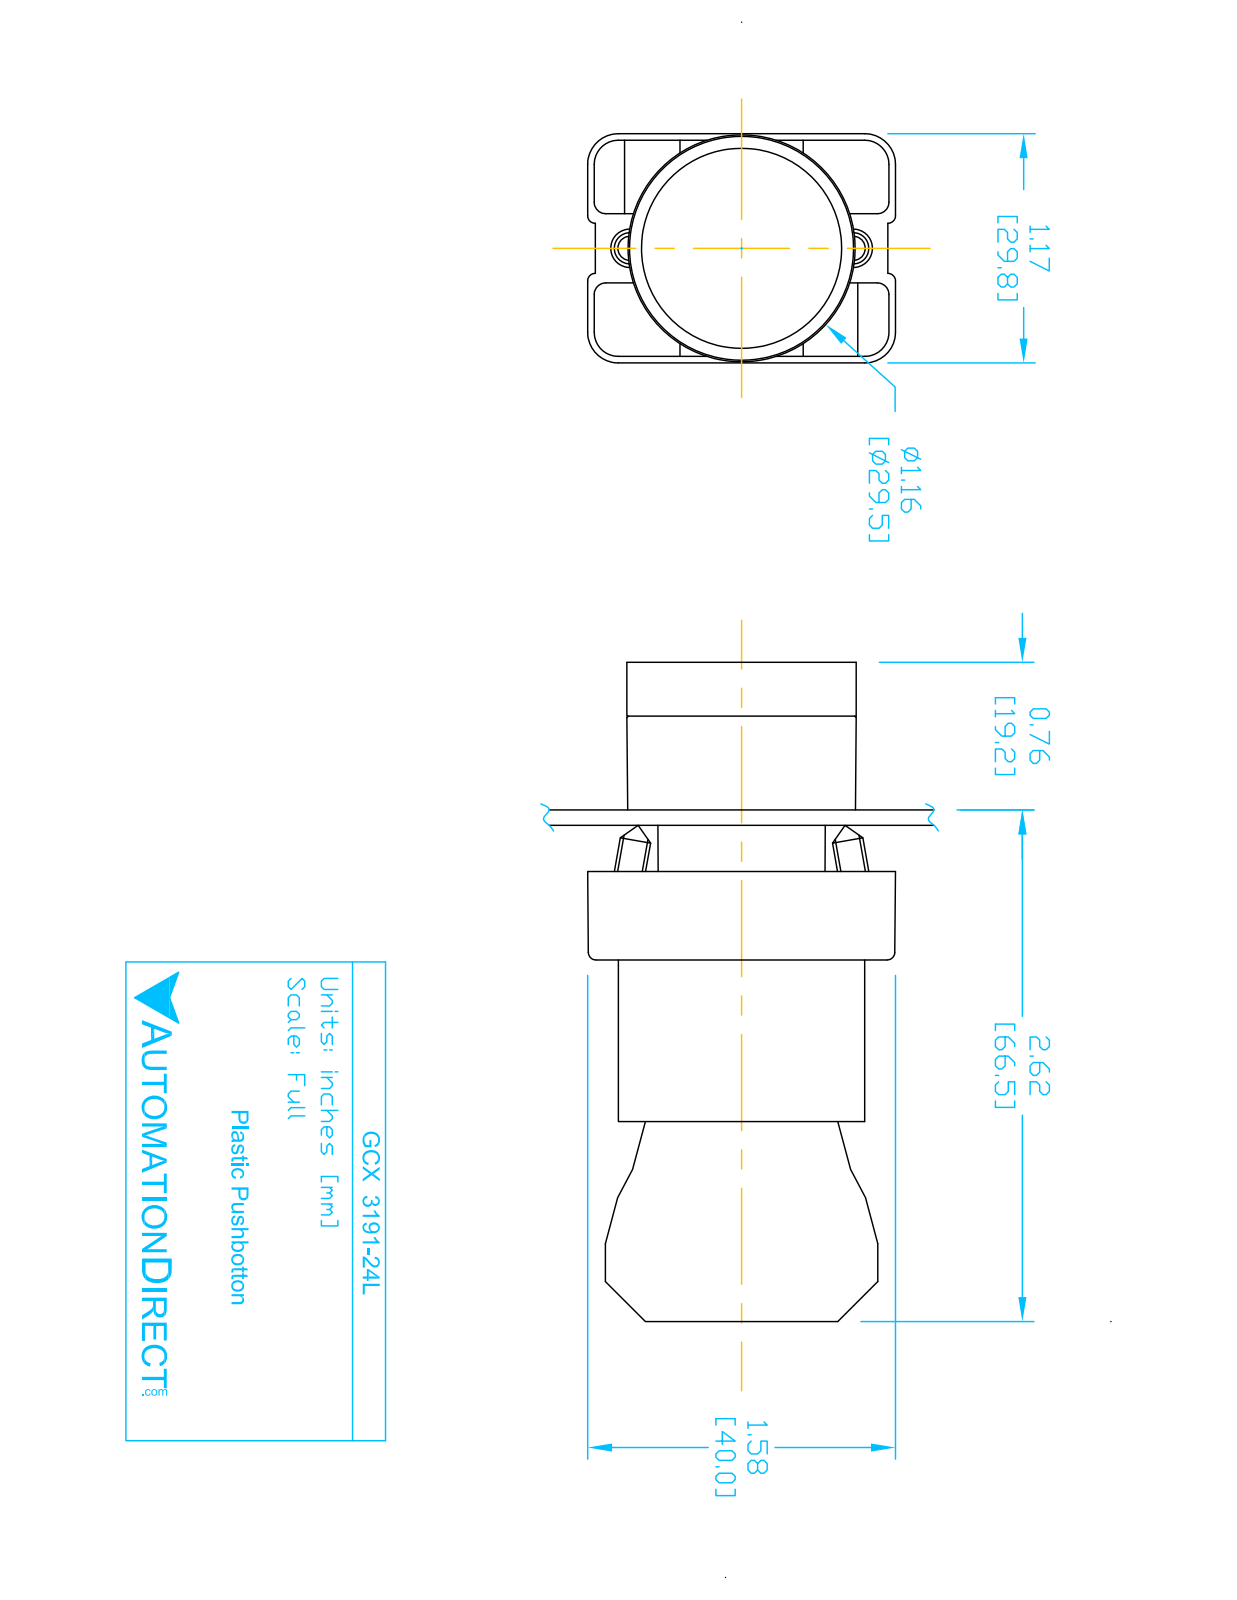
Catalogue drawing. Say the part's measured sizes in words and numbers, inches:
The part is named "CONTACT BLOCK; GCX3191-24L; ECX3029-2; ECX1050 (+1 more)". Its 3-D file was written by "SolidWorks 2016 (AUTOMOTIVE_DESIGN)". It is 8 solids with 431 faces: 252 planar, 148 cylindrical and 31 other. Overall it measures 3.319 by 1.581 by 1.177 inches. Its volume is 2.794 cubic inches and its surface area 38.77 square inches. Round holes: 2 of diameter 0.079, 2 of diameter 0.124, 2 of diameter 0.13, 1 of diameter 0.087, 1 of diameter 0.197, 1 of diameter 0.469, 1 of diameter 0.878, 1 of diameter 0.888, 1 of diameter 1.024. Round bosses or shafts: 4 of diameter 0.157, 1 of diameter 1.175, 1 of diameter 1.004, 1 of diameter 0.945, 1 of diameter 0.856, 1 of diameter 0.78, 1 of diameter 0.504. Partial cylindrical surfaces (rounded edges, fillets, slot ends): 24 of radius 0.059, 12 of radius 0.041, 12 of radius 0.124, 12 of radius 0.157, 8 of radius 0.039, 2 of radius 0.128, 1 of radius 0.02, 1 of radius 0.063. The main face-to-face distances are 0.827, 0.579, 2.02, 1.193, 1.171, 0.276, 2.295, 1.469, 0.031, 0.033. The hole center spacings are 0.236, 0.544, 0.472, 0.49.
